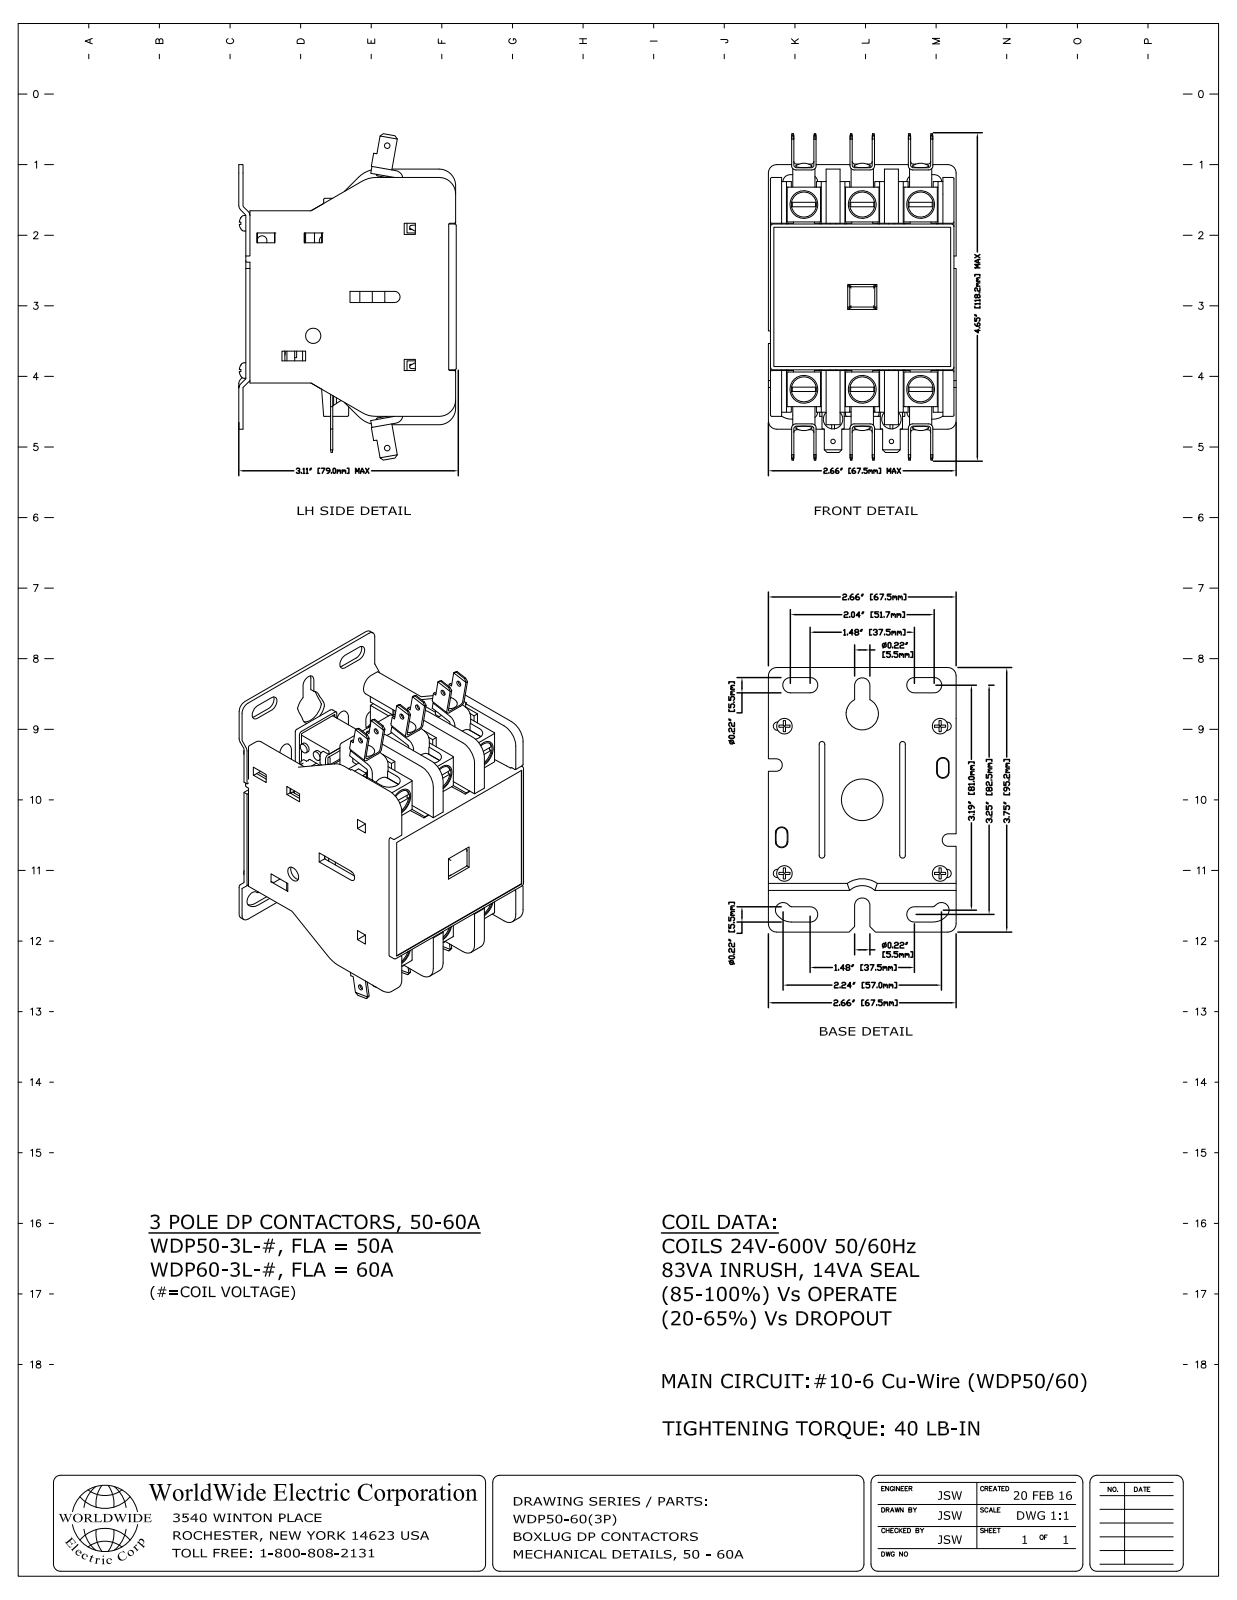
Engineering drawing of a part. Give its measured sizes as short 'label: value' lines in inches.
name: WDP50-3L-120
written by: SolidWorks 2017 (AUTOMOTIVE_DESIGN)
unit: in
bodies: 5 solids, 3094 faces (1931 planar, 804 cylindrical, 359 other)
size: 3.748 × 2.874 × 2.657
volume: 8.221 in³; area: 151.4 in²
holes: 10× ⌀0.094, 5× ⌀0.197, 4× ⌀0.071, 3× ⌀0.15, 2× ⌀0.079, 2× ⌀0.276, 1× ⌀0.457, 1× ⌀0.591
bosses: 12× ⌀0.138, 10× ⌀0.22, 9× ⌀0.197, 9× ⌀0.15, 6× ⌀0.256, 6× ⌀0.244, 2× ⌀0.354, 2× ⌀0.213
rounds: 178× R0.02, 55× R0.039, 52× R0.079, 31× R0.059, 18× R0.031, 16× R0.108, 10× R0.046, 6× R0.089
face distances: 0.157, 0.059, 0.039, 0.748, 2.441, 0.63, 0.098, 1.417, 0.591, 1.535
hole spacings: 0.787, 0.474, 0.707, 0.847, 0.848, 0.933, 1.046, 1.087
